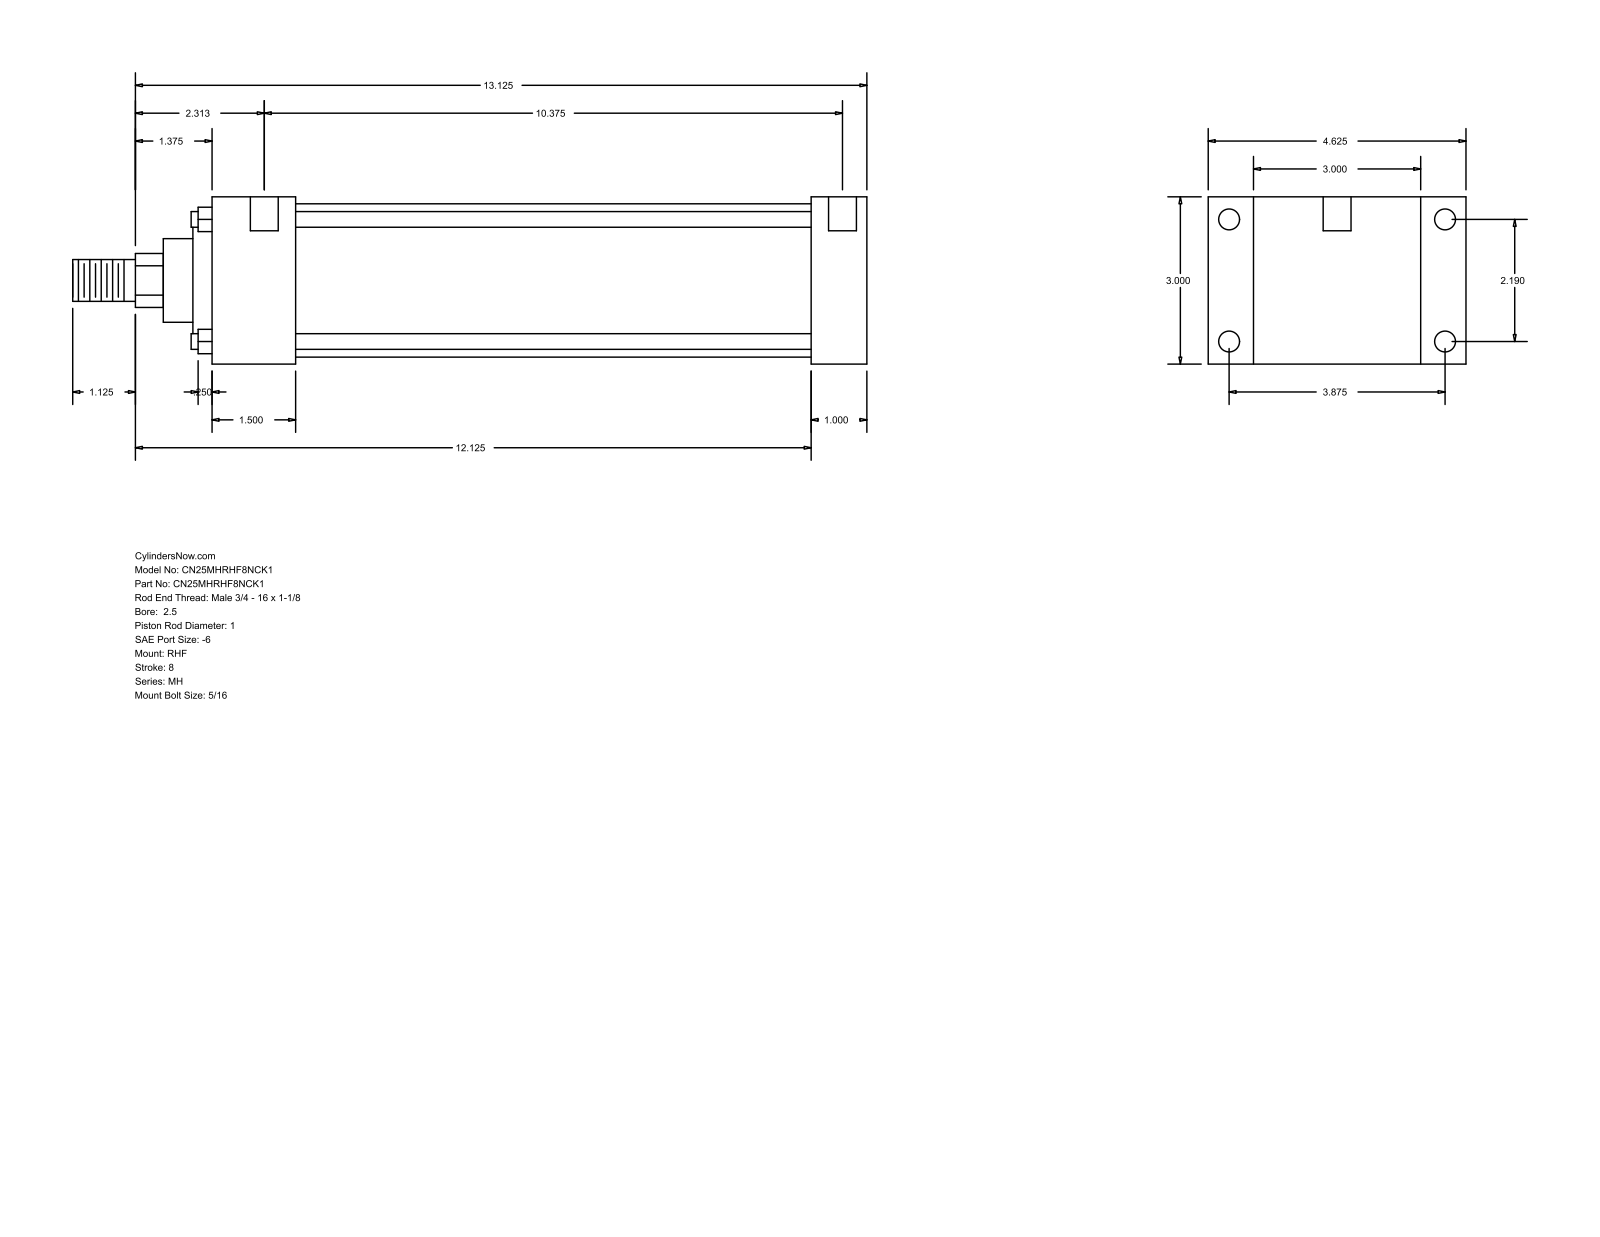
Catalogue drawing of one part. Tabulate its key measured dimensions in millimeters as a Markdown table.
| quantity | value |
| --- | --- |
| part name | MH_RHF__0250_1 |
| STEP written by | GSSL Pune (CONFIG_CONTROL_DESIGN) |
| units | millimeters |
| bodies | 0 solids, 90 faces (61 planar, 29 cylindrical, 0 other) |
| overall size | 361.95 × 117.47 × 76.2 |
| round holes (diameter × count) | 5.56 × 4, 9.53 × 4, 12.7 × 2 |
| round bosses / shafts (diameter × count) | 7.14 × 4, 69.85 × 1, 60.33 × 1, 38.1 × 1, 25.4 × 1, 19.05 × 1 |
| partial cylindrical surfaces (radius × count) | 12.29 × 1 |
| main face-to-face distances | 76.2, 25.4, 20.64, 96.84, 273.06, 298.46, 117.48, 38.11, 234.95, 260.35 |
| hole center spacings | 55.62, 98.42, 113.05, 271.46, 3.18, 4.76, 263.52, 266.7 |
